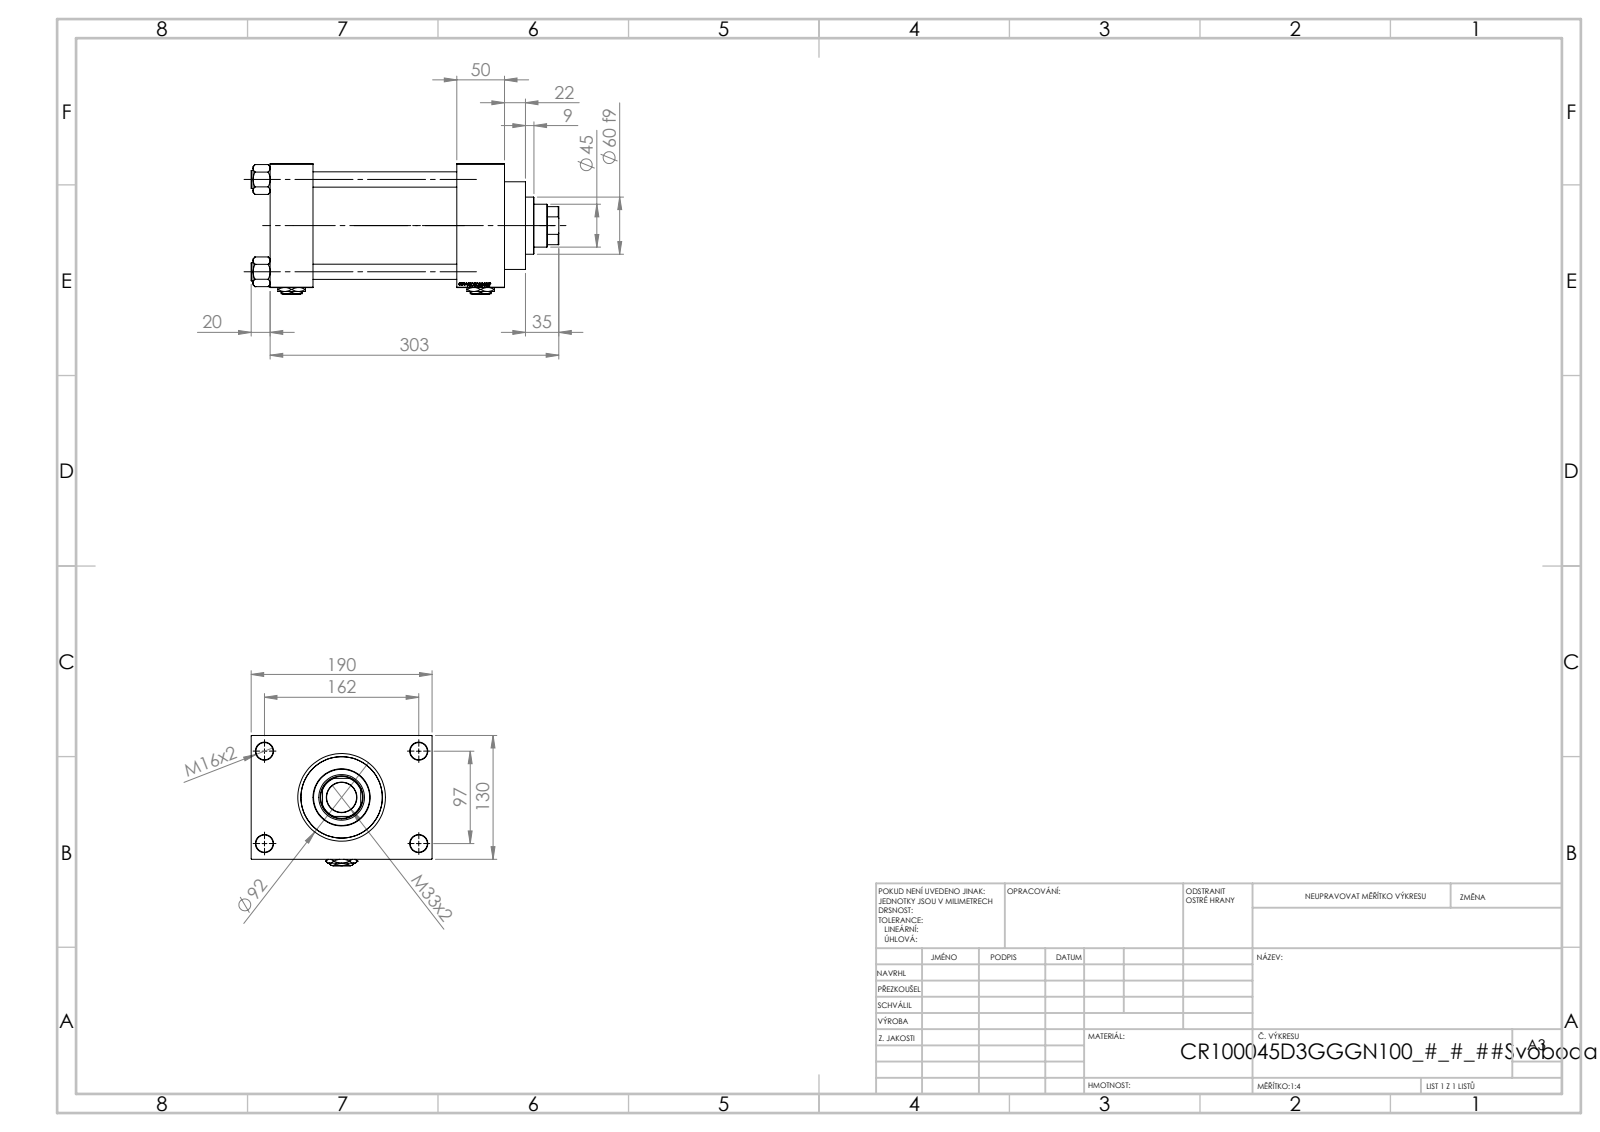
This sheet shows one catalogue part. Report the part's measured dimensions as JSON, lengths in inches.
{"part_name": "Zatka_pro_OIL_PORT; V215CR_VCP_D; V215CR_D_TYCINKA; V215CR_D_Body (+2 more)", "step_written_by": "SolidWorks 2019 (CONFIG_CONTROL_DESIGN)", "units": "inches", "bodies": {"solids": 13, "faces": 1253, "planar": 593, "cylindrical": 100, "other": 560}, "overall_size": [12.717, 7.48, 5.394], "volume_in3": 174.6, "surface_area_in2": 679.6, "round_holes": [[0.63, 4], [0.709, 4], [0.276, 2], [1.041, 2], [1.378, 2], [1.24, 1], [1.772, 1], [1.89, 1], [2.992, 1], [3.366, 1], [3.937, 1]], "round_bosses_or_shafts": [[0.748, 4], [4.173, 1], [3.622, 1], [2.362, 1]], "partial_cylinders_radius": [[0.866, 1]], "face_to_face_distances": [5.118, 1.772, 7.717, 5.945, 9.685, 7.913, 1.969, 1.181, 6.299, 7.48], "hole_center_spacings": [1.281, 2.698, 3.717, 3.815, 4.026, 5.096, 6.367, 3.819]}
